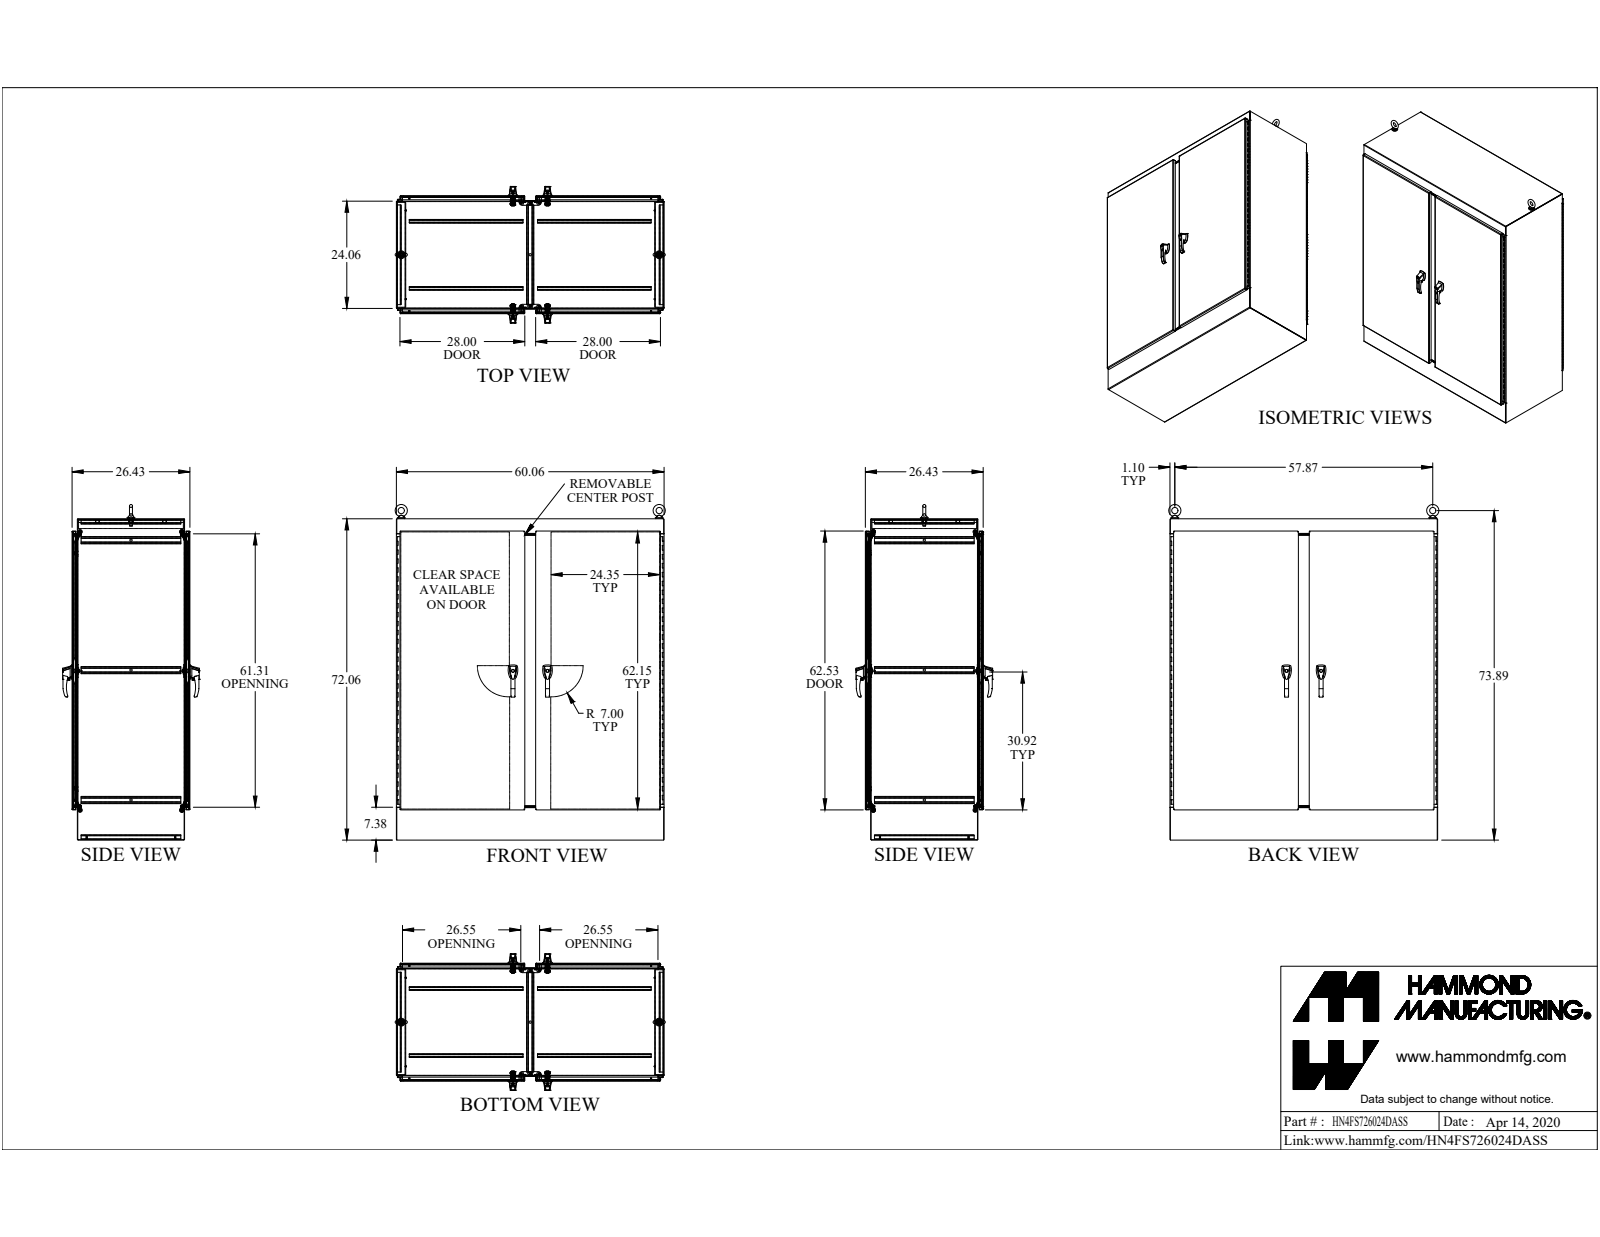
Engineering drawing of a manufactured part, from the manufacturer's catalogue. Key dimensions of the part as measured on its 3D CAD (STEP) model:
Part name (STEP PRODUCT): HN4FS726024DASS
STEP written by: SolidWorks 2019 (CONFIG_CONTROL_DESIGN)
Units: inches
Bodies: 189 solids, 5411 faces (2809 planar, 2126 cylindrical, 476 other)
Overall size (bounding box): 75.256 × 60.604 × 30.664
Volume: 1 934 in³ · Surface area: 40 818 in²
Round holes (diameter × count): ⌀0.304 ×20, ⌀0.25 ×12, ⌀0.313 ×8, ⌀0.35 ×8, ⌀0.201 ×6, ⌀0.257 ×6, ⌀0.28 ×6, ⌀0.281 ×6, ⌀0.313 ×6, ⌀0.39 ×6, ⌀0.413 ×6, ⌀0.11 ×4
Round bosses / shafts (diameter × count): ⌀0.75 ×8, ⌀0.44 ×8, ⌀1 ×6, ⌀0.63 ×6, ⌀0.313 ×6, ⌀0.293 ×6, ⌀0.25 ×6, ⌀0.246 ×6
Partial cylindrical surfaces — rounded edges, fillets, slot ends (radius × count): R0.043 ×60, R0.018 ×52, R0.138 ×48, R0.1 ×46, R0.5 ×46, R0.125 ×42, R0.06 ×39, R0.318 ×32
Main face-to-face distances: 0.095, 26.339, 26.244, 26.434, 59.965, 1.187, 25.152, 71.965, 59.87, 60.06
Hole centre spacings: 6, 58.636, 12, 59.55, 18, 61.043, 24, 63.073
